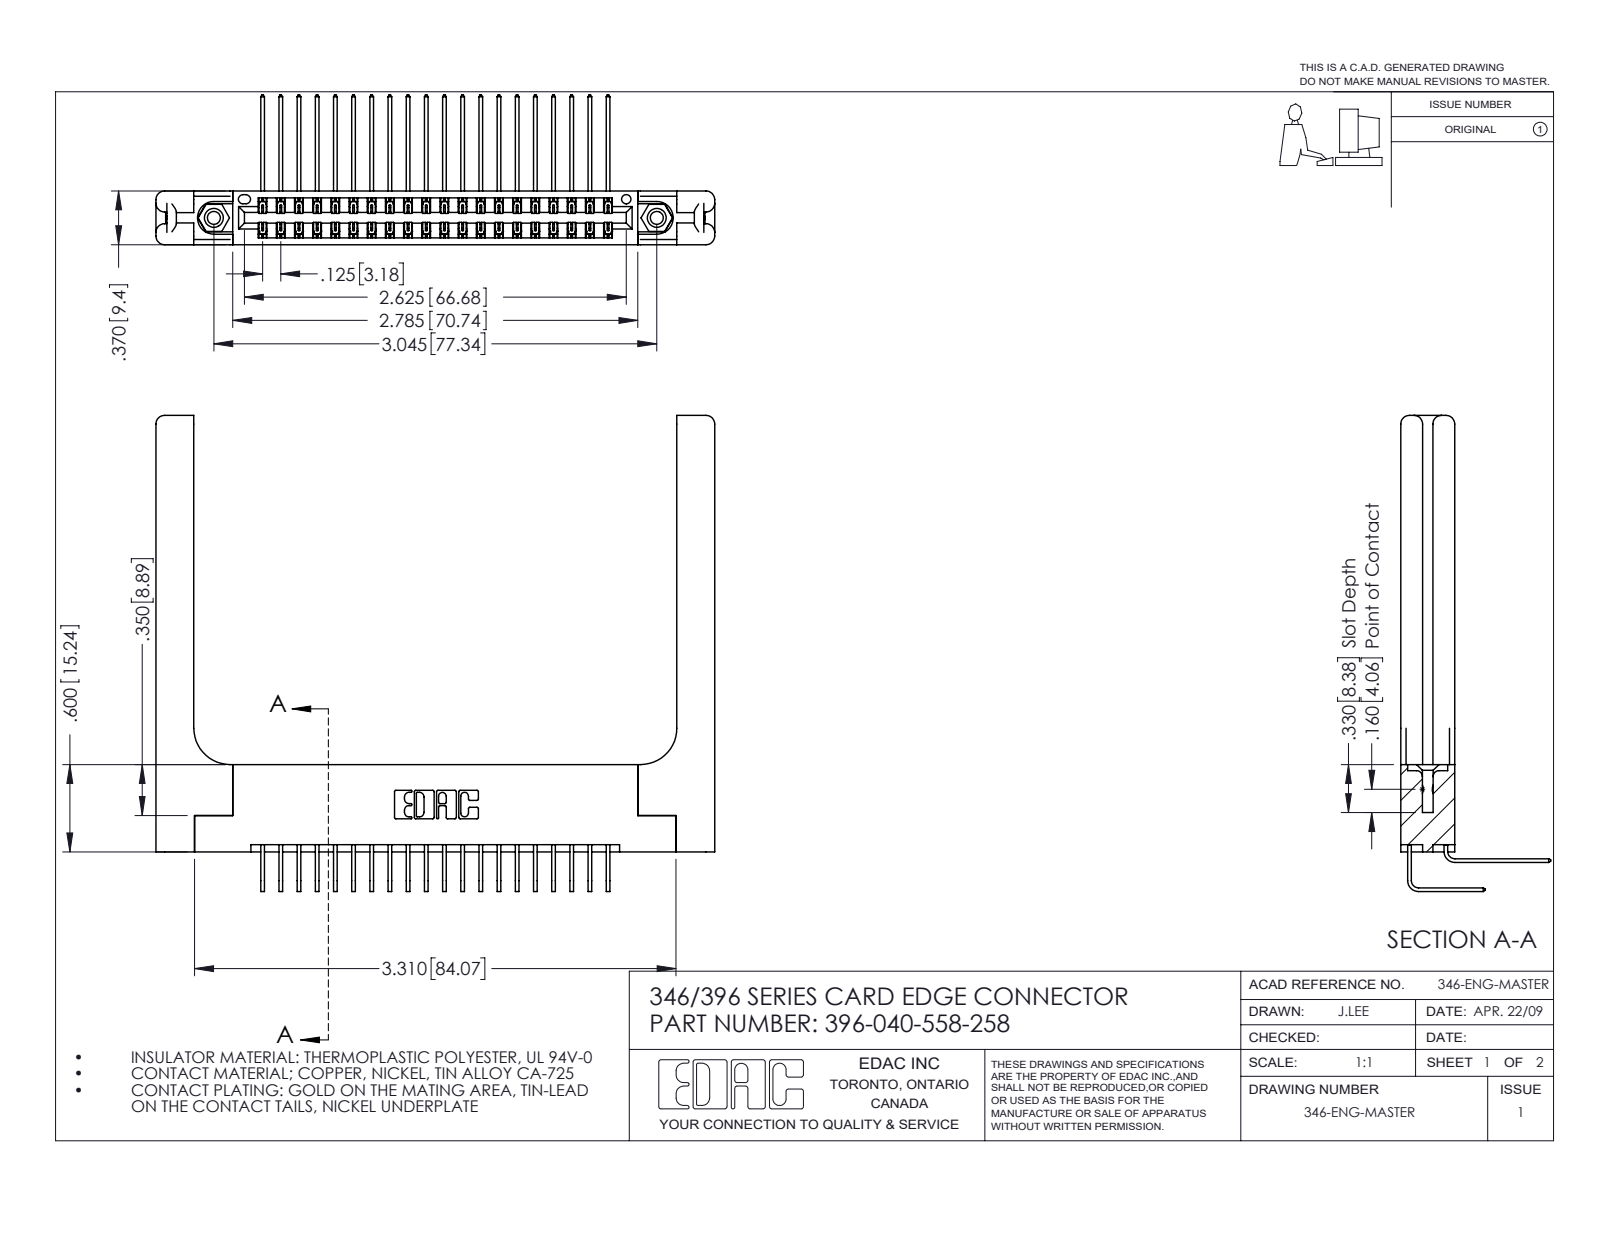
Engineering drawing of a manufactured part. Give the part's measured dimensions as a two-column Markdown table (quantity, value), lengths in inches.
| quantity | value |
| --- | --- |
| part name | 345-292-001_558 Tail - 2; 346-220-058_345-220-058; 345-250-001_345-250-001-102; 396-040-558-258 (+2 more) |
| STEP written by | SolidWorks 2016 (CONFIG_CONTROL_DESIGN) |
| units | inches |
| bodies | 45 solids, 2538 faces (1704 planar, 774 cylindrical, 60 other) |
| overall size | 3.841 × 3.273 × 1.03 |
| volume | 1.042 in³ |
| surface area | 29.28 in² |
| round holes (diameter × count) | 0.089 × 2, 0.125 × 2, 0.156 × 2, 0.064 × 1 |
| round bosses / shafts (diameter × count) | 0.155 × 2 |
| partial cylindrical surfaces (radius × count) | 0.006 × 60, 0.01 × 22, 0.06 × 16, 0.007 × 6, 0.031 × 6, 0.026 × 3, 0.014 × 2, 0.022 × 2 |
| main face-to-face distances | 0.37, 0.322, 0.072, 0.048, 0.15, 0.148, 0.025, 0.298, 0.25, 0.077 |
| hole center spacings | 0.246, 2.837, 3.045 |
